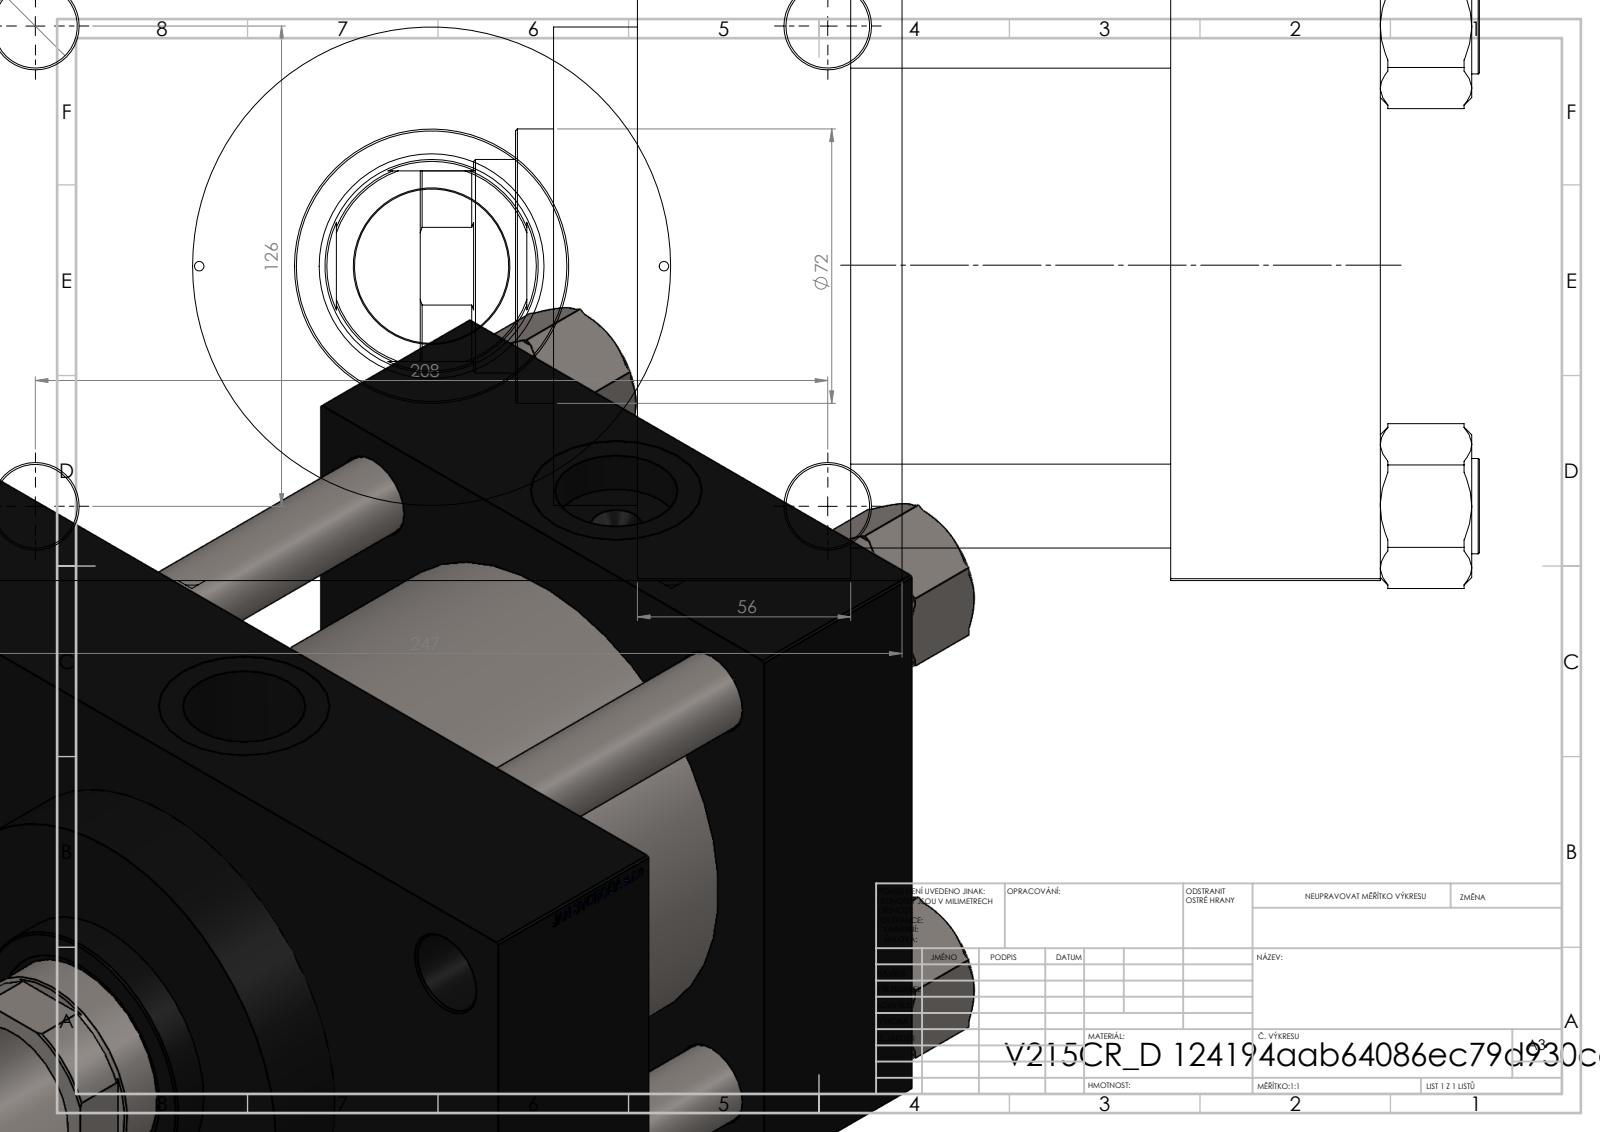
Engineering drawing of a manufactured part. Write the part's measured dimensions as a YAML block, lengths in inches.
part_name: "V215CR_VCP_D; V215_VC_A; V215CR_D_TYCINKA; NUT_M5_D (+1 more)"
step_written_by: "SolidWorks 2019 (CONFIG_CONTROL_DESIGN)"
units: inches
bodies: {solids: 11, faces: 1155, planar: 546, cylindrical: 91, other: 518}
overall_size: [10.945, 9.724, 6.659]
volume: 302.6
surface_area: 821.5
round_holes:
  - {diameter: 0.866, count: 8}
  - {diameter: 0.098, count: 2}
  - {diameter: 0.276, count: 2}
  - {diameter: 1.269, count: 2}
  - {diameter: 1.772, count: 2}
  - {diameter: 1.594, count: 1}
  - {diameter: 2.205, count: 1}
  - {diameter: 2.323, count: 1}
  - {diameter: 3.78, count: 1}
  - {diameter: 4.921, count: 1}
  - {diameter: 4.941, count: 1}
round_bosses_or_shafts:
  - {diameter: 0.984, count: 4}
  - {diameter: 5.157, count: 1}
  - {diameter: 2.835, count: 1}
partial_cylinders:
  - {radius: 1.063, count: 1}
face_to_face_distances: [6.496, 3.307, 2.165, 5.472, 2.205, 7.677, 5.512, 1.614, 8.11, 6.84]
hole_center_spacings: [1.616, 2.48, 3.003, 3.505, 4.787, 4.957, 5.215, 5.473]
